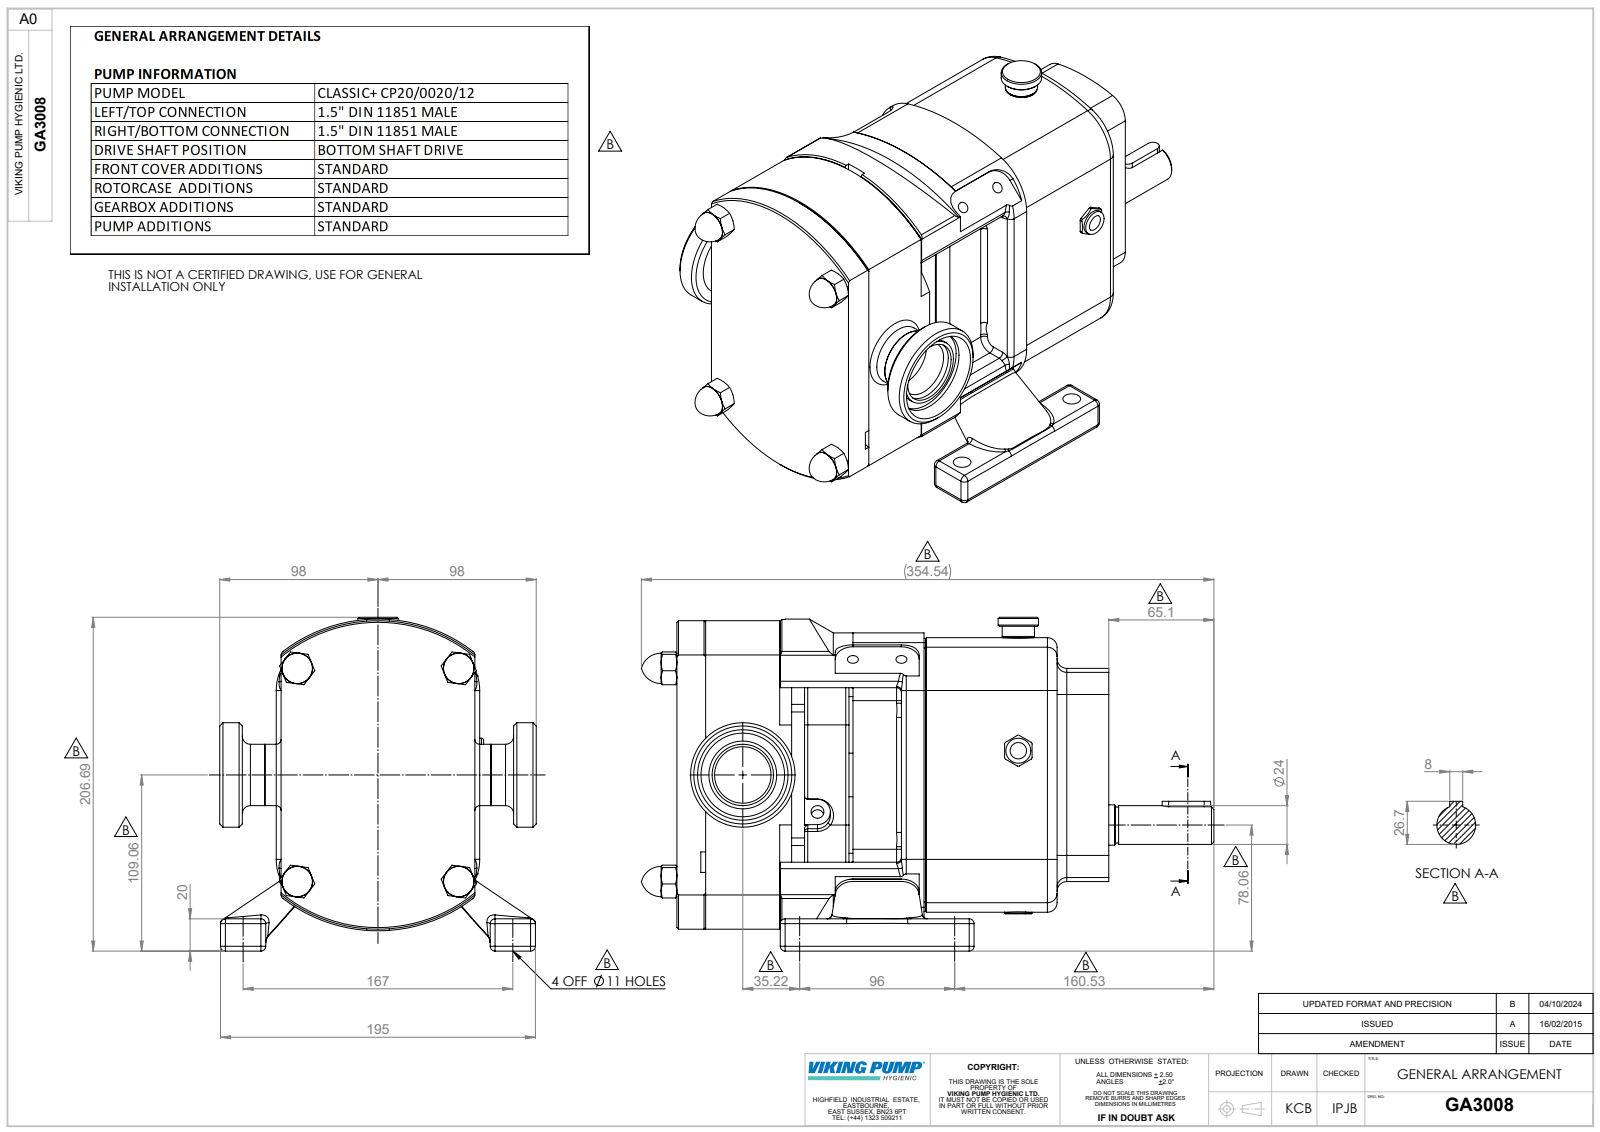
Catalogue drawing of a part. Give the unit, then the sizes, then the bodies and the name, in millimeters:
Units: millimetres
Overall size (bounding box): 354.54 × 206.69 × 196
Round holes (diameter × count): ⌀6.8 ×4, ⌀11 ×4, ⌀6.47 ×3, ⌀8 ×2, ⌀22.53 ×1, ⌀35 ×1, ⌀51.8 ×1
Round bosses / shafts (diameter × count): ⌀35 ×2, ⌀17 ×2, ⌀64.7 ×1, ⌀42 ×1, ⌀38 ×1, ⌀25.02 ×1, ⌀25 ×1, ⌀24 ×1
Partial cylindrical surfaces — rounded edges, fillets, slot ends (radius × count): R3 ×55, R2 ×18, R1 ×16, R6 ×8, R11.1 ×8, R1.27 ×6, R4 ×6, R8 ×6
Main face-to-face distances: 120, 109.04, 158.4, 267.44, 25, 95, 20.27, 99.73, 4.73, 74.73
Hole centre spacings: 53.7, 30.05, 92.35, 96, 167.02, 61.08, 159.1, 159.11
Volume: 4 786 000 mm³ · Surface area: 305 958 mm²
Bodies: 3 solids, 839 faces (257 planar, 296 cylindrical, 286 other)
Part name (STEP PRODUCT): Copy (2) of CP20-0020-12 H B^GA3008; Copy of Z94-5031-22 - 1.5 INCH DIN11851^GA3008; GA3008
STEP written by: SolidWorks 2023 (AUTOMOTIVE_DESIGN)
